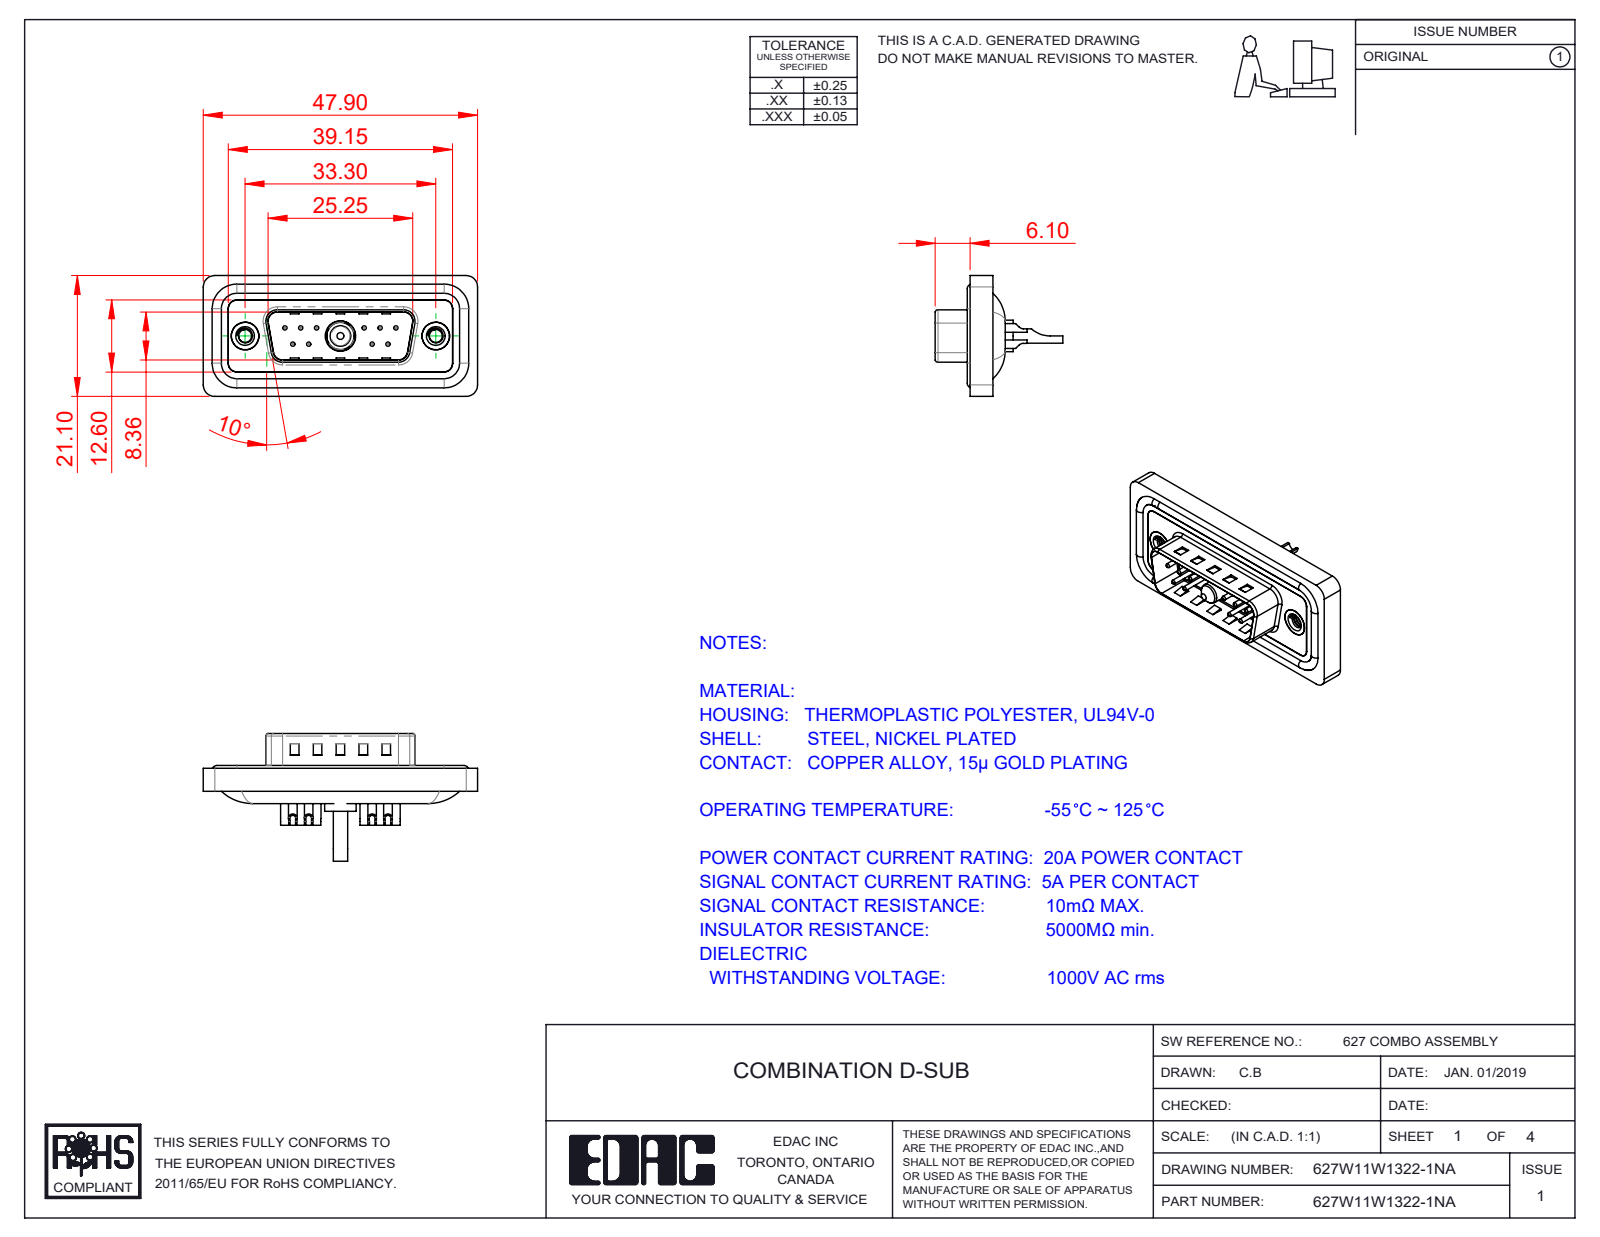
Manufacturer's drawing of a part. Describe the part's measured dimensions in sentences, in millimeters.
The part is named "627Combo Shell Rear_15 Contacts; 627Combo Threaded Rivet_A; 627Combo Housing_11W1; 627Combo Waterproof Housing_15 Contacts (+5 more)". Its 3-D file was written by "SolidWorks 2020 (CONFIG_CONTROL_DESIGN)". It is 19 solids with 872 faces: 288 planar, 372 cylindrical and 212 other. Overall it measures 47.9 by 22.3 by 21.1 millimeters. Its volume is 5 462 cubic millimeters and its surface area 8 961 square millimeters. Round holes: 10 of diameter 0.75, 10 of diameter 1, 10 of diameter 1.6, 10 of diameter 2, 2 of diameter 2.26, 2 of diameter 4, 2 of diameter 4.8, 2 of diameter 5, 1 of diameter 1.7, 1 of diameter 4.85, 1 of diameter 5.3. Round bosses or shafts: 10 of diameter 1.5, 4 of diameter 1.6, 2 of diameter 4.9, 1 of diameter 5.5, 1 of diameter 5.2, 1 of diameter 4.75, 1 of diameter 3.75, 1 of diameter 3.6. Partial cylindrical surfaces (rounded edges, fillets, slot ends): 26 of radius 1.5, 20 of radius 2, 9 of radius 1, 8 of radius 0.5, 8 of radius 1.6, 4 of radius 0.25, 4 of radius 0.6, 4 of radius 0.65. The main face-to-face distances are 0.4, 1.1, 1.6, 1.5, 0.5, 2.9, 3.1, 2.5, 4.1, 0.82. The hole center spacings are 3.16, 2.77, 13.85, 11.08, 16.62, 5.03, 5.04, 5.54.
